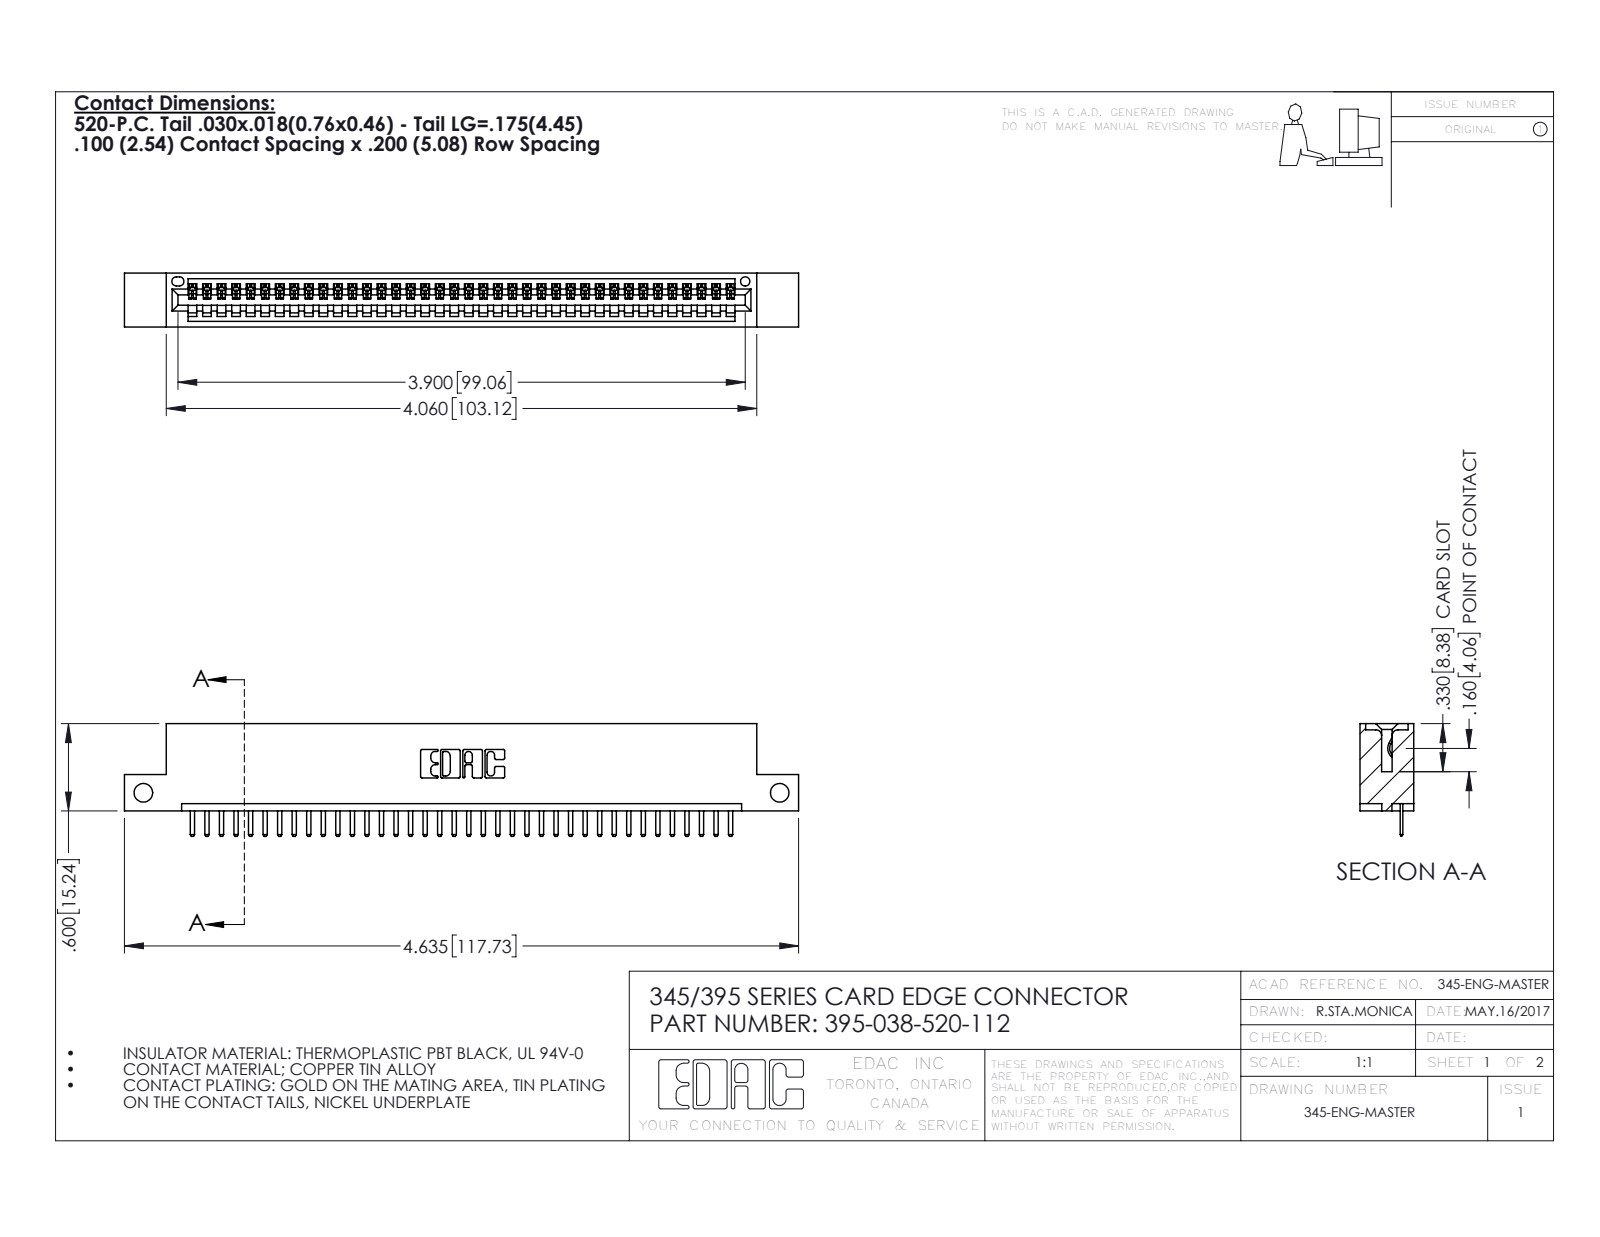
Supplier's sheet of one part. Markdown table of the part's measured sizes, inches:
| quantity | value |
| --- | --- |
| part name | 345 Part_Flush Mounting Lugs - Side Mount; 395-038-520-112; 345-292-001_345-293-120 |
| STEP written by | SolidWorks 2016 (CONFIG_CONTROL_DESIGN) |
| units | inches |
| bodies | 39 solids, 2482 faces (1676 planar, 806 cylindrical, 0 other) |
| overall size | 4.635 × 0.775 × 0.37 |
| volume | 0.668 in³ |
| surface area | 21.7 in² |
| round holes (diameter × count) | 0.128 × 2, 0.064 × 1 |
| partial cylindrical surfaces (radius × count) | 0.01 × 78, 0.006 × 76, 0.01 × 22, 0.007 × 6, 0.031 × 6, 0.026 × 3, 0.031 × 2, 0.04 × 2 |
| main face-to-face distances | 0.298, 0.072, 0.37, 0.2, 0.098, 0.272, 0.025, 0.225, 0.072, 0.149 |
| hole center spacings | 4.375 |
